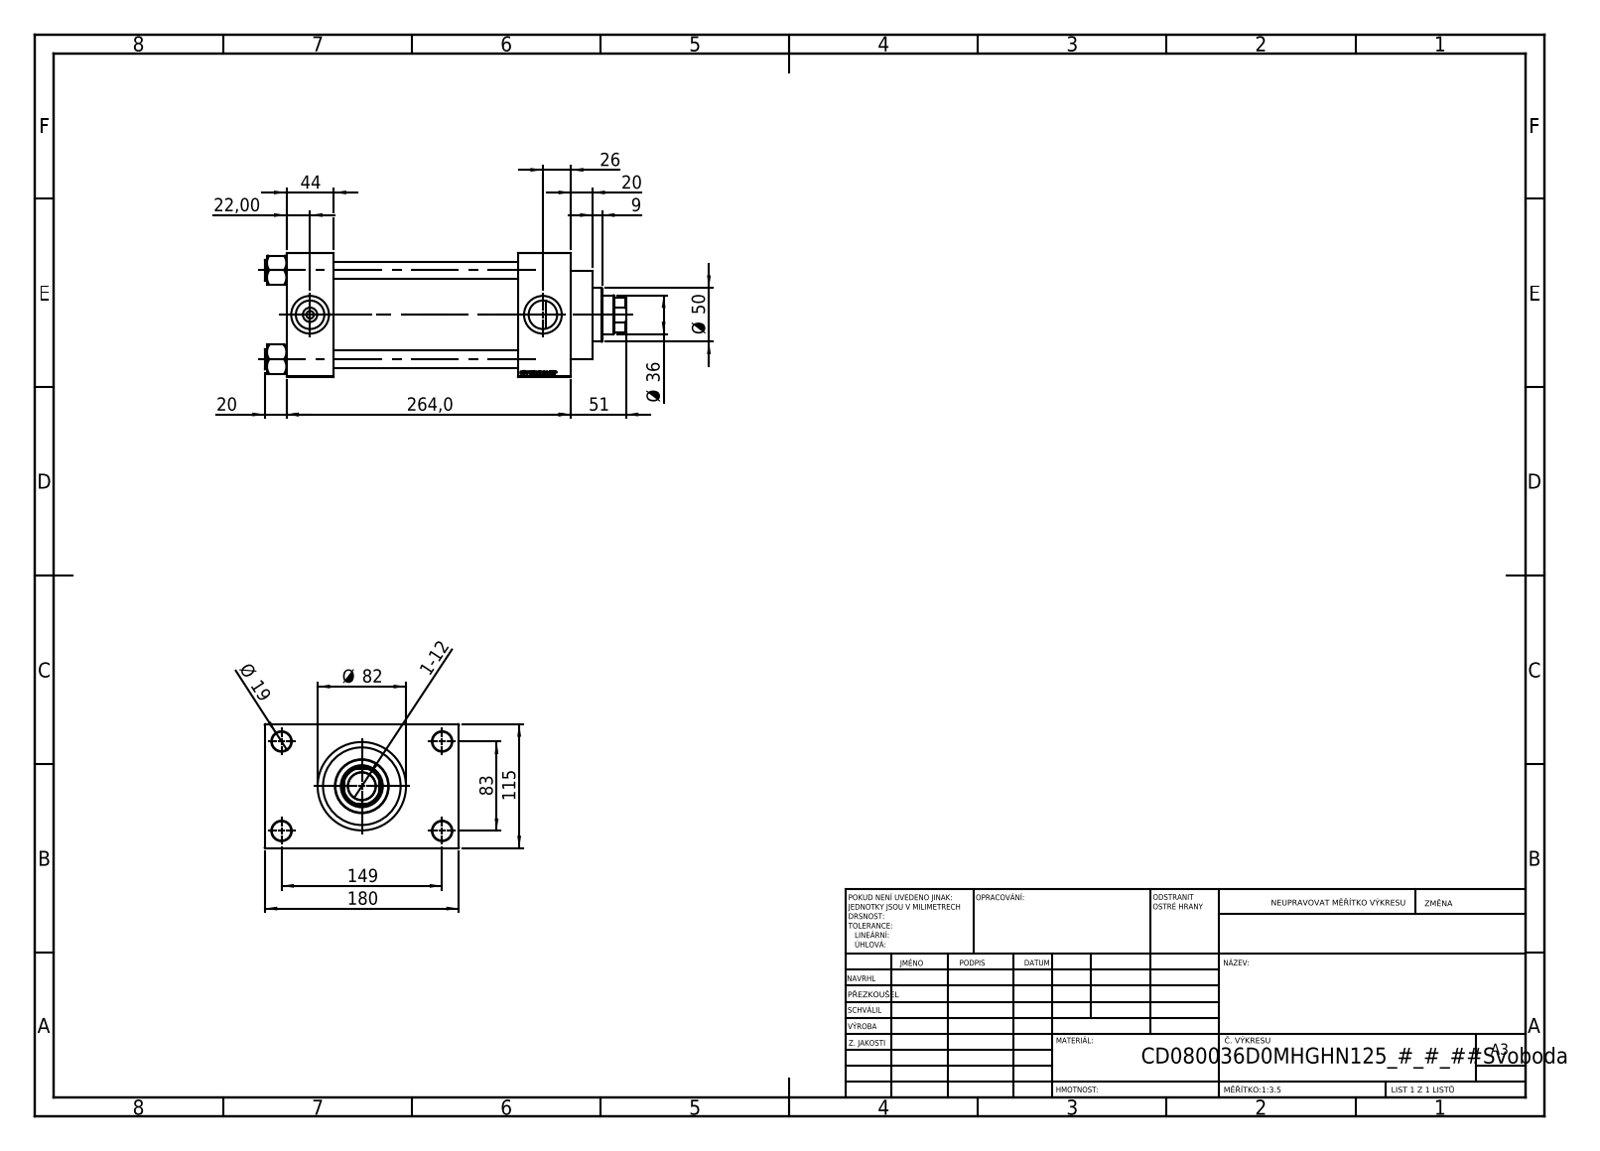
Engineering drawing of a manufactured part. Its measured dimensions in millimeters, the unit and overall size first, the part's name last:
Units: millimetres
Overall size (bounding box): 335 × 180 × 115
Round holes (diameter × count): ⌀16 ×4, ⌀18 ×4, ⌀7 ×2, ⌀26.44 ×2, ⌀35 ×2, ⌀25.5 ×1, ⌀36 ×1, ⌀39 ×1, ⌀61 ×1, ⌀72 ×1, ⌀80 ×1
Round bosses / shafts (diameter × count): ⌀19 ×4, ⌀86 ×1, ⌀82 ×1, ⌀50 ×1
Partial cylindrical surfaces — rounded edges, fillets, slot ends (radius × count): R17.5 ×1
Main face-to-face distances: 115, 171, 220, 49, 44, 215, 264, 32.5, 147.5, 180
Hole centre spacings: 33.15, 58.48, 82.7, 85.28, 89.24, 115.85, 142.43, 83
Volume: 2 253 000 mm³ · Surface area: 384 339 mm²
Bodies: 11 solids, 1151 faces (545 planar, 88 cylindrical, 518 other)
Part name (STEP PRODUCT): V215CD_VC_A; V215CD_NUT_M5_D; V215CD_D_Body; V215CD_VCP_D (+1 more)
STEP written by: SolidWorks 2019 (CONFIG_CONTROL_DESIGN)
